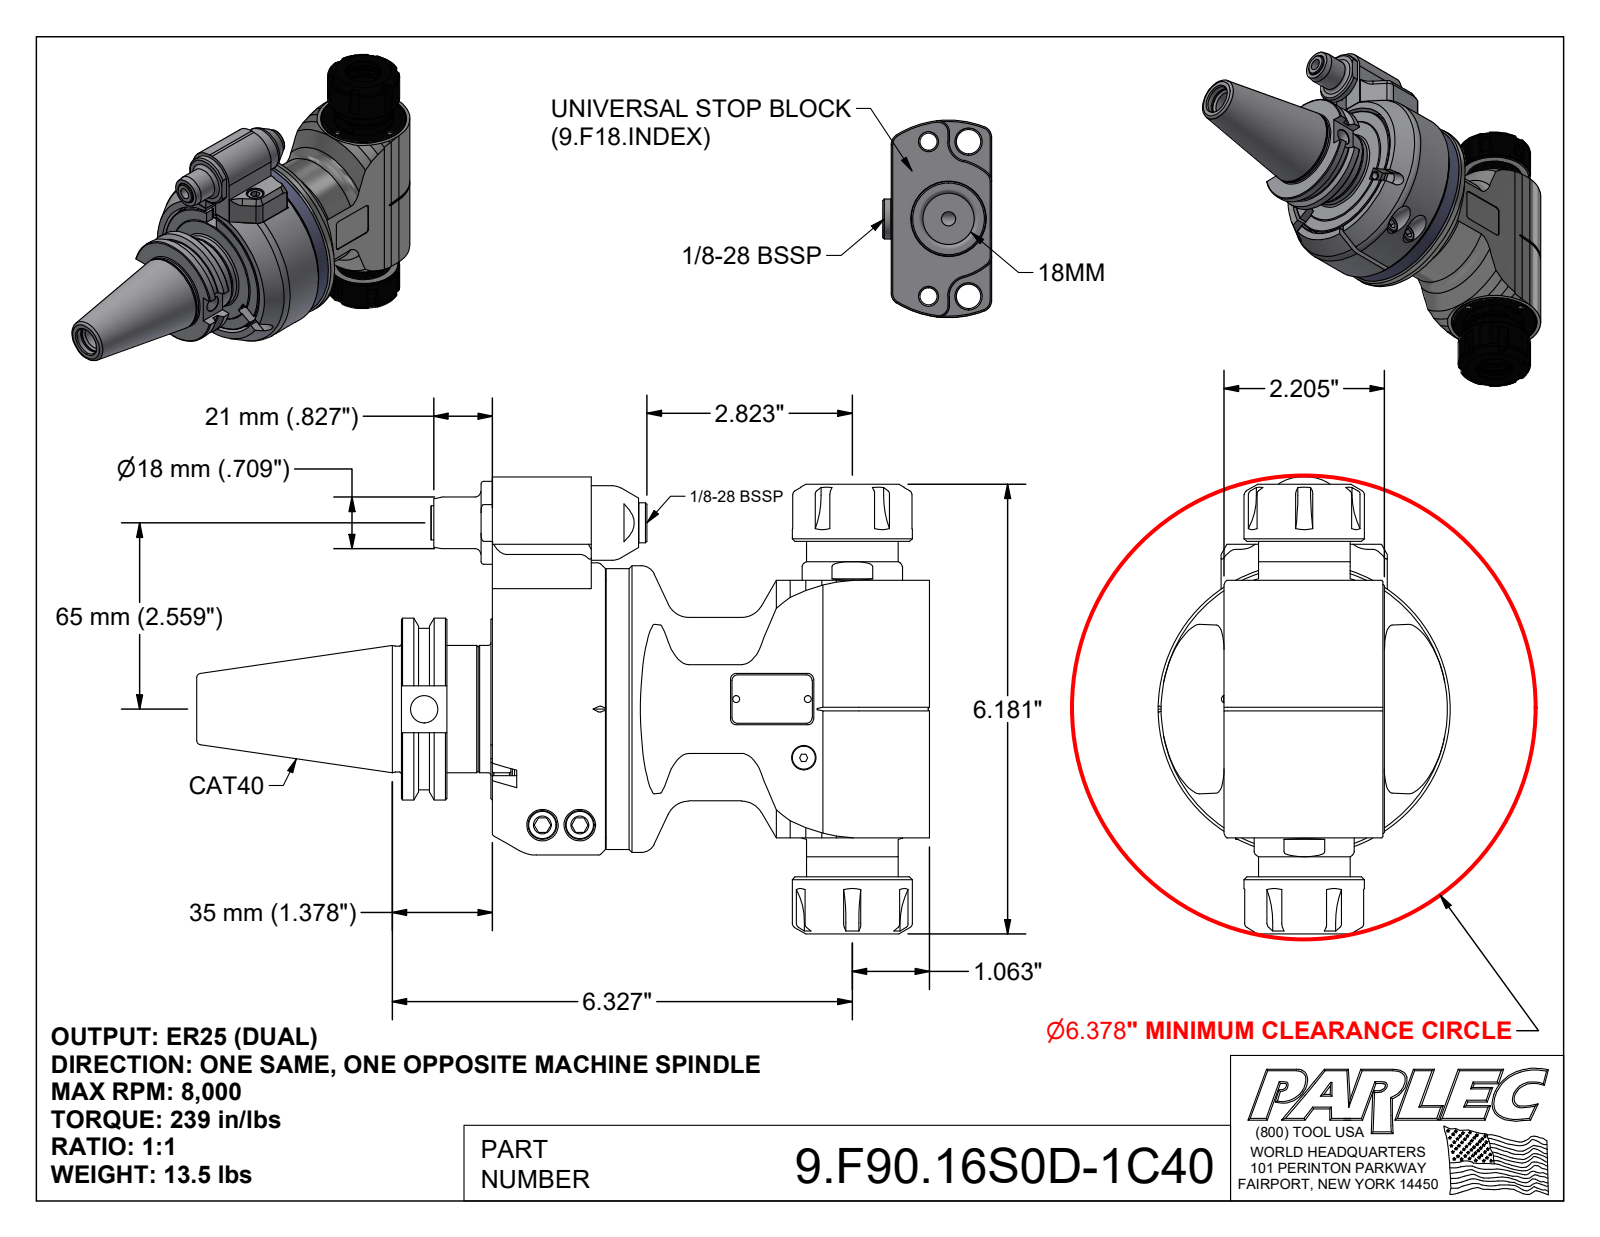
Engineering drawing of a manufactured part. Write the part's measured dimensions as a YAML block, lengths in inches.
part_name: "9.F90.16S0D-1C40; 9_F90_16S00_2U; 9_GA"
step_written_by: "Autodesk Inventor 2025 (AUTOMOTIVE_DESIGN)"
units: inches
bodies: {solids: 4, faces: 706, planar: 312, cylindrical: 183, other: 211}
overall_size: [10.077, 6.28, 4.016]
volume: 61.71
surface_area: 234.3
round_holes:
  - {diameter: 0.126, count: 8}
  - {diameter: 0.197, count: 3}
  - {diameter: 0.256, count: 3}
  - {diameter: 0.102, count: 2}
  - {diameter: 0.13, count: 2}
  - {diameter: 0.165, count: 2}
  - {diameter: 0.315, count: 2}
  - {diameter: 0.409, count: 2}
  - {diameter: 0.433, count: 2}
  - {diameter: 0.492, count: 2}
  - {diameter: 1.063, count: 2}
  - {diameter: 0.098, count: 1}
round_bosses_or_shafts:
  - {diameter: 0.394, count: 4}
  - {diameter: 0.709, count: 2}
  - {diameter: 0.472, count: 2}
  - {diameter: 0.315, count: 2}
  - {diameter: 0.236, count: 2}
  - {diameter: 0.098, count: 2}
  - {diameter: 4.016, count: 1}
  - {diameter: 3.937, count: 1}
partial_cylinders:
  - {radius: 0.039, count: 14}
  - {radius: 0.079, count: 12}
  - {radius: 0.984, count: 12}
  - {radius: 0.118, count: 6}
  - {radius: 0.157, count: 4}
  - {radius: 0.016, count: 2}
  - {radius: 0.02, count: 2}
  - {radius: 0.315, count: 2}
face_to_face_distances: [0.276, 0.02, 1.252, 0.335, 1.555, 1.28, 1.299, 0.059, 0.303, 1.22]
hole_center_spacings: [0.325, 0.459, 0.846, 1.197, 0.276, 0.504, 0.65, 0.74]
